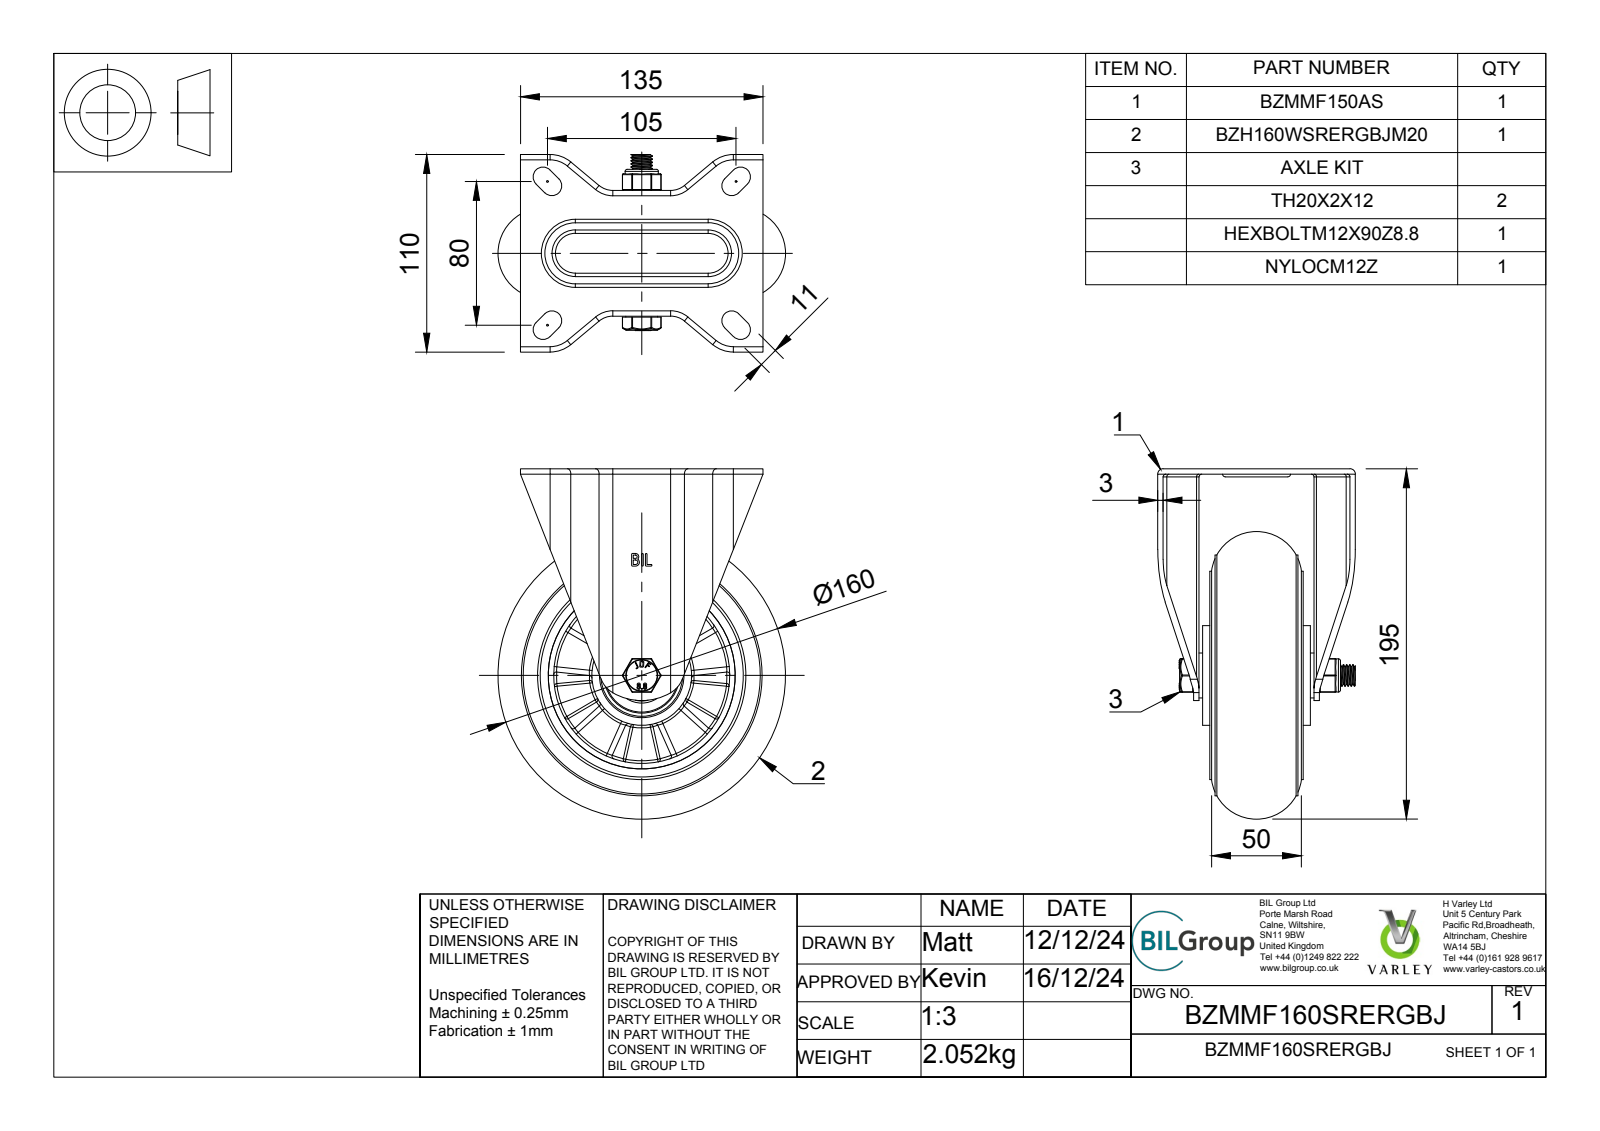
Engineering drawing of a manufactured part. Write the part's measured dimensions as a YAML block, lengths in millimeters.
part_name: "BZMMF160SRERGBJ v3; BZMMF150AS - 64 v1; ZINC PLATED, PRESSED STEEL BRACKET; BZH160WSRERGBJM20 v1 (+7 more)"
step_written_by: "Autodesk Translation Framework v13.20.0.188 (AP242_MANAGED_MODEL_BASED_3D_ENGINEERING_MIM_LF)"
units: millimeters
bodies: {solids: 35, faces: 1359, planar: 457, cylindrical: 244, other: 658}
overall_size: [195, 160, 110]
volume: 751192
surface_area: 251342
round_holes:
  - {diameter: 12, count: 1}
  - {diameter: 12.2, count: 1}
  - {diameter: 12.25, count: 1}
  - {diameter: 14, count: 1}
  - {diameter: 20, count: 1}
  - {diameter: 28.5, count: 1}
  - {diameter: 30.8, count: 1}
  - {diameter: 40.3, count: 1}
  - {diameter: 40.5, count: 1}
  - {diameter: 42, count: 1}
  - {diameter: 47, count: 1}
  - {diameter: 98, count: 1}
round_bosses_or_shafts:
  - {diameter: 134, count: 1}
  - {diameter: 116, count: 1}
  - {diameter: 55.5, count: 1}
  - {diameter: 40.8, count: 1}
  - {diameter: 31.3, count: 1}
  - {diameter: 27, count: 1}
  - {diameter: 25, count: 1}
  - {diameter: 24, count: 1}
partial_cylinders:
  - {radius: 0.5, count: 20}
  - {radius: 1.5, count: 12}
  - {radius: 3, count: 8}
  - {radius: 5.5, count: 8}
  - {radius: 0.47, count: 4}
  - {radius: 0.9, count: 4}
  - {radius: 2, count: 4}
  - {radius: 6, count: 4}
face_to_face_distances: [3, 67, 10, 50, 7, 17, 24.74, 70, 60, 5]
